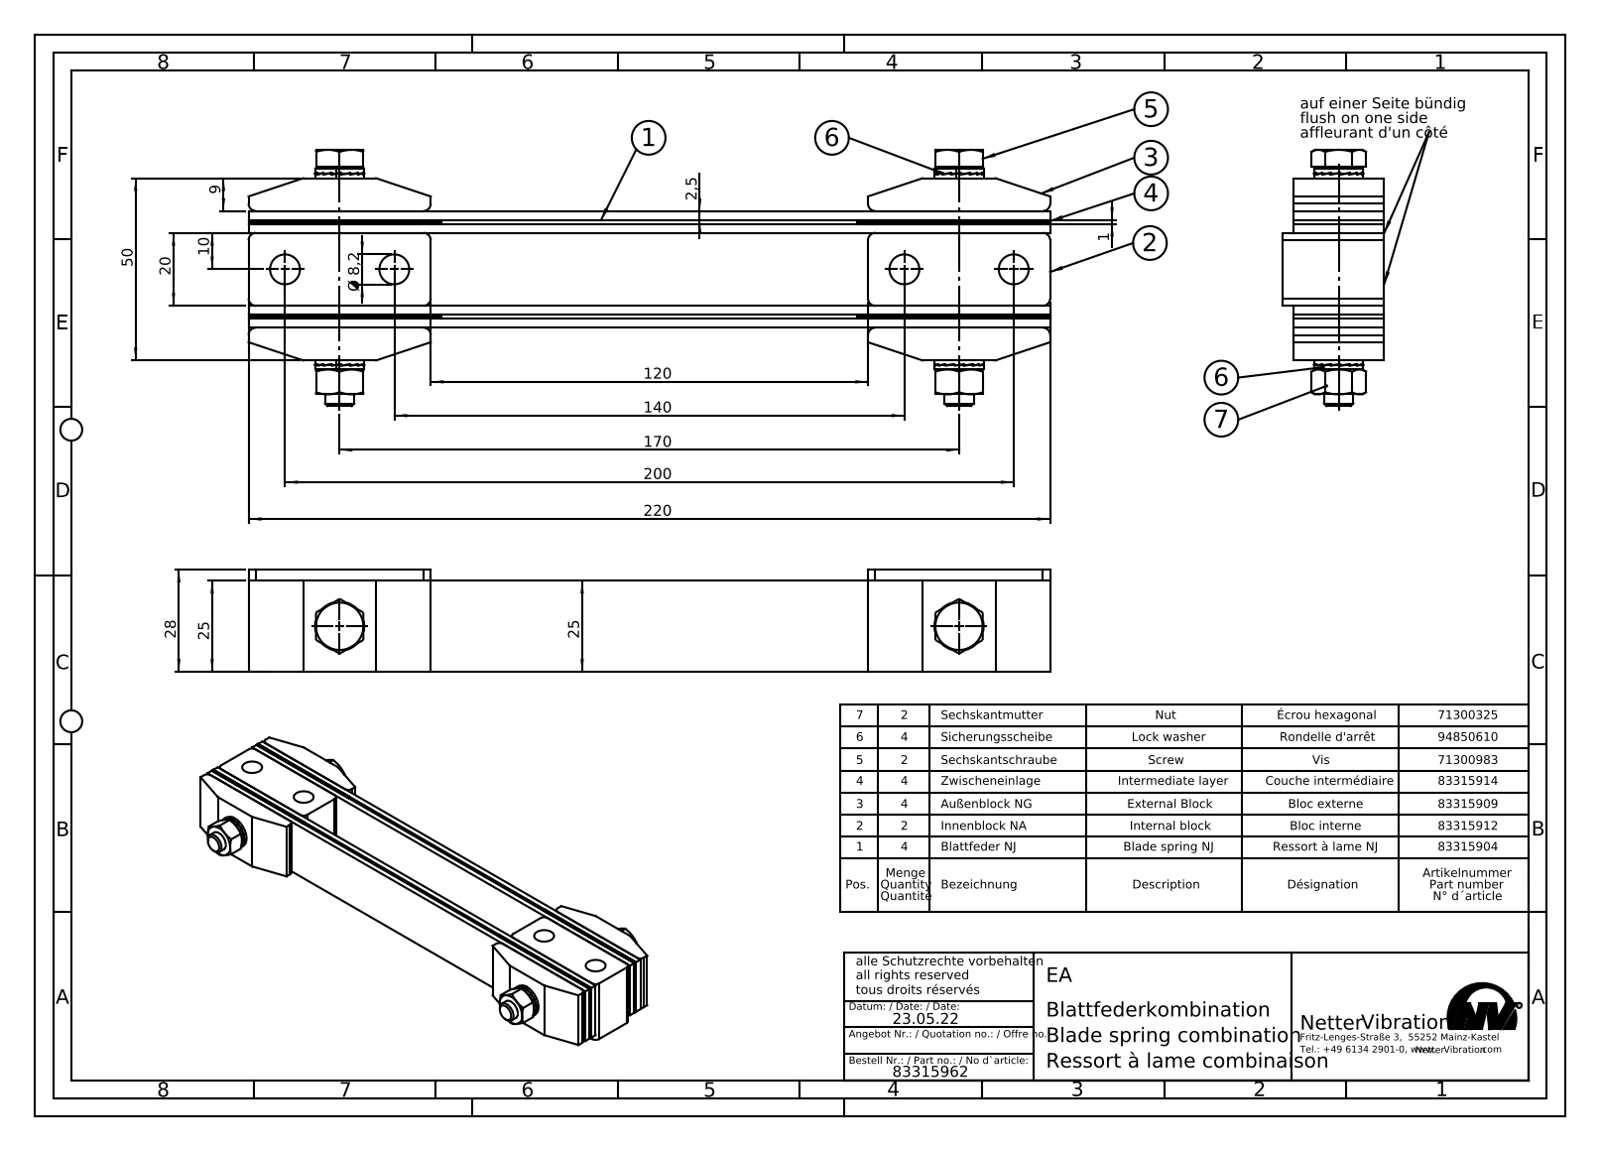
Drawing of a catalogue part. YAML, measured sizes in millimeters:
part_name: "Blattfederkombination EA # 83315962"
step_written_by: "SolidWorks 2015 (CONFIG_CONTROL_DESIGN)"
units: millimeters
bodies: {solids: 22, faces: 746, planar: 594, cylindrical: 100, other: 52}
overall_size: [220, 70.3, 28]
volume: 152523
surface_area: 95745
round_holes:
  - {diameter: 8.2, count: 6}
  - {diameter: 6.8, count: 2}
  - {diameter: 8, count: 2}
  - {diameter: 8.5, count: 2}
  - {diameter: 8.7, count: 2}
round_bosses_or_shafts:
  - {diameter: 13.5, count: 2}
  - {diameter: 13, count: 2}
partial_cylinders:
  - {radius: 2, count: 16}
face_to_face_distances: [2.5, 26, 3.5, 1, 23.5, 22.5, 6, 28.5, 29.5, 25]
hole_center_spacings: [170, 30, 140, 200]
